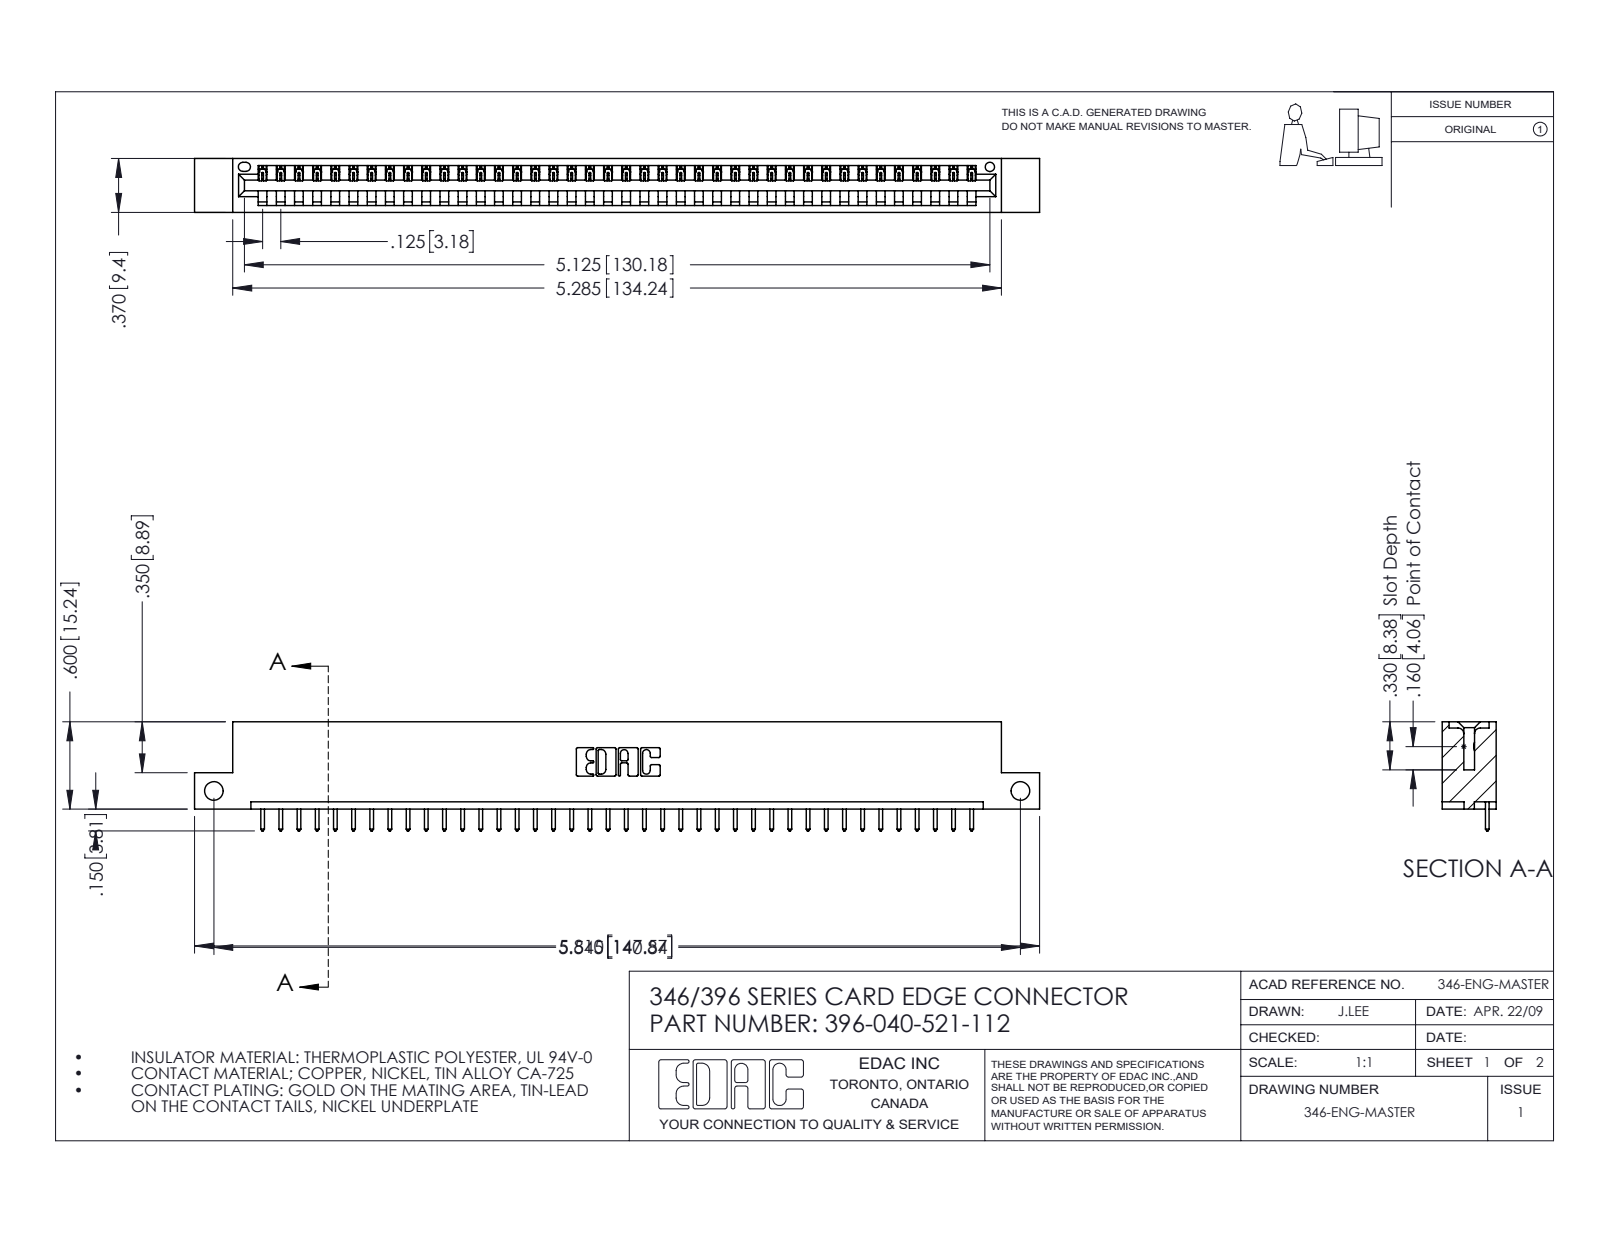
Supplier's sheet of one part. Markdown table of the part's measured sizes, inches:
| quantity | value |
| --- | --- |
| part name | 396-040-521-112; 345-292-001_345-293-121; 346 Part_Flush Mounting Lugs - Side Mount |
| STEP written by | SolidWorks 2016 (CONFIG_CONTROL_DESIGN) |
| units | inches |
| bodies | 41 solids, 2442 faces (1676 planar, 766 cylindrical, 0 other) |
| overall size | 5.81 × 0.75 × 0.37 |
| volume | 0.849 in³ |
| surface area | 25.99 in² |
| round holes (diameter × count) | 0.128 × 2, 0.064 × 1 |
| partial cylindrical surfaces (radius × count) | 0.006 × 80, 0.01 × 80, 0.01 × 22, 0.007 × 6, 0.031 × 6, 0.026 × 3, 0.031 × 2, 0.04 × 2 |
| main face-to-face distances | 0.048, 0.322, 0.37, 0.25, 0.072, 0.298, 0.025, 0.148, 0.222, 0.1 |
| hole center spacings | 5.545 |
